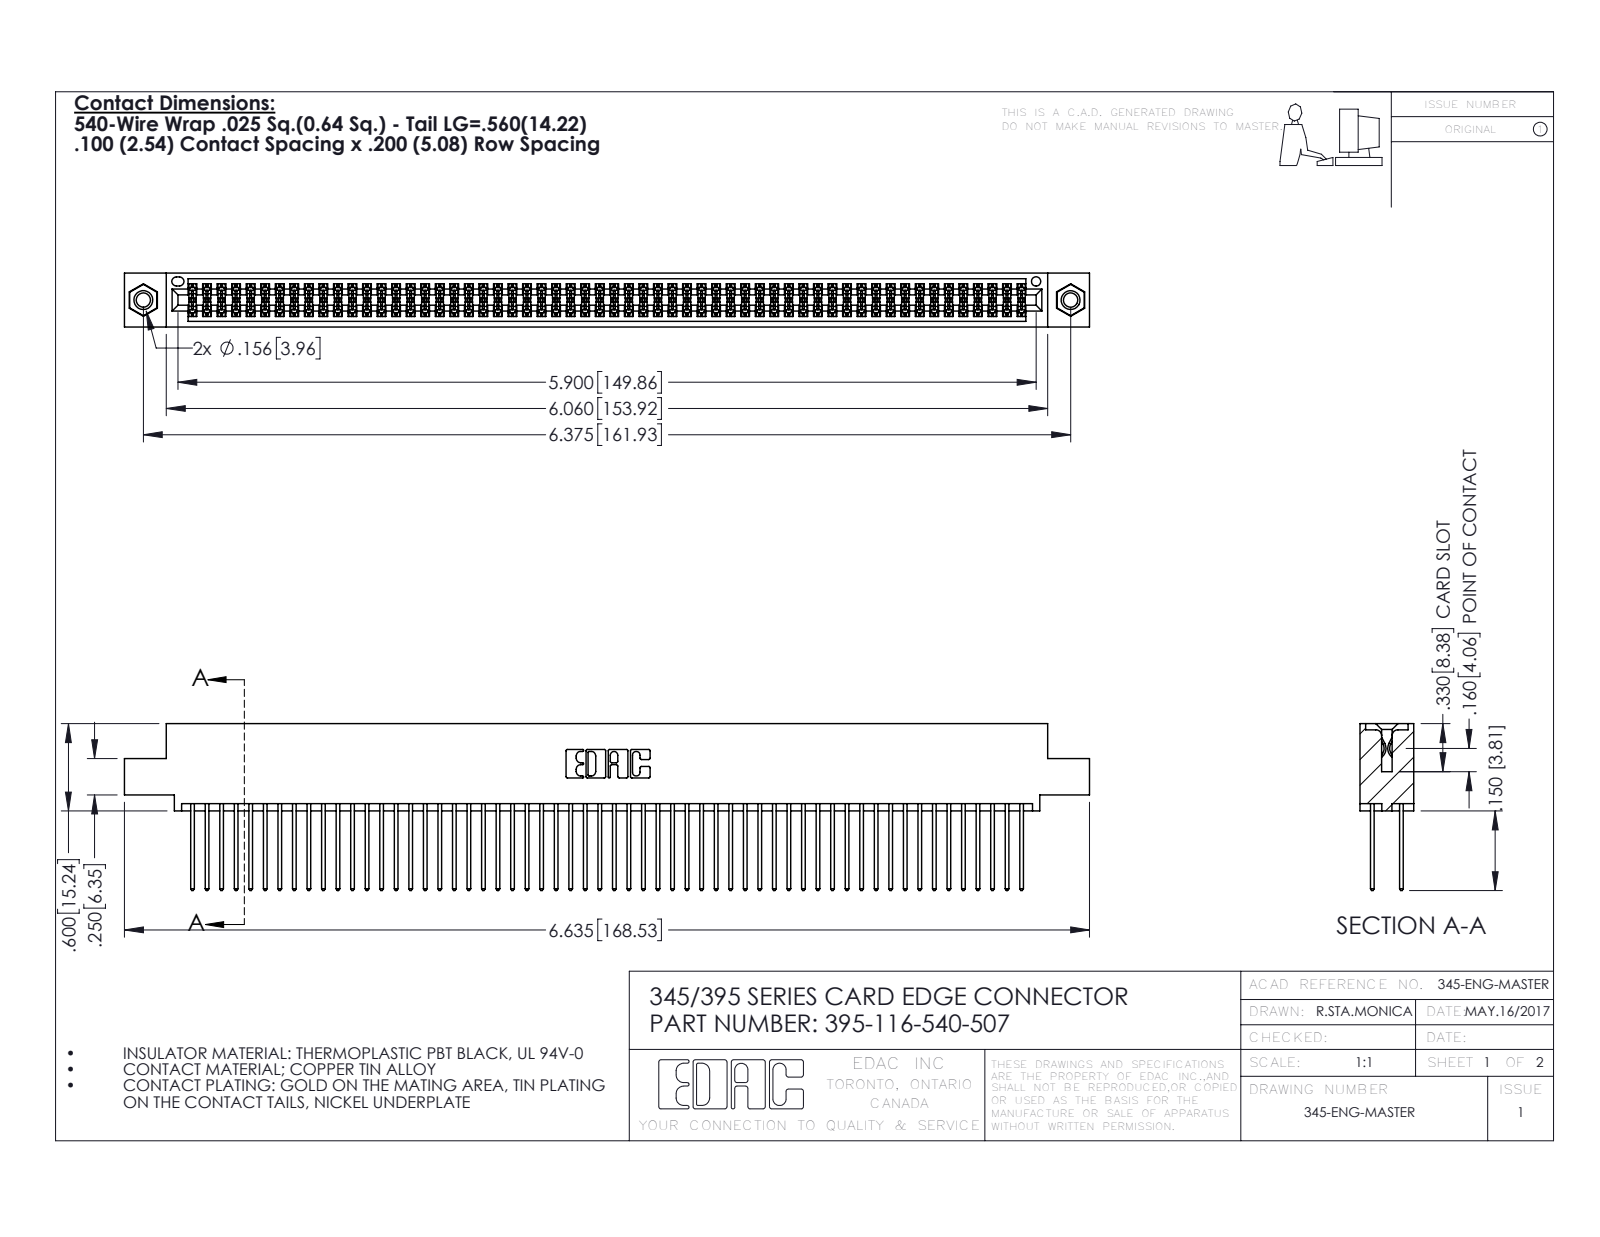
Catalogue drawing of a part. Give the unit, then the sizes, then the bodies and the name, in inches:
Units: inches
Overall size (bounding box): 6.635 × 1.147 × 0.37
Round holes (diameter × count): ⌀0.098 ×2, ⌀0.125 ×2, ⌀0.156 ×2, ⌀0.064 ×1
Round bosses / shafts (diameter × count): ⌀0.155 ×2
Partial cylindrical surfaces — rounded edges, fillets, slot ends (radius × count): R0.006 ×174, R0.01 ×116, R0.01 ×22, R0.007 ×6, R0.031 ×6, R0.026 ×3, R0.014 ×2, R0.019 ×2
Main face-to-face distances: 0.072, 0.298, 0.2, 0.098, 0.272, 0.025, 0.37, 0.225, 0.175, 0.149
Hole centre spacings: 0.27, 6.139, 6.375
Volume: 1.03 in³ · Surface area: 42.49 in²
Bodies: 119 solids, 5990 faces (3944 planar, 2030 cylindrical, 16 other)
Part name (STEP PRODUCT): 345 Part_0.110 Offset - 0.156 Dia-TI; 345-250-001_345-250-005-103; 395-116-540-507; 345-292-001_345-293-140
STEP written by: SolidWorks 2016 (CONFIG_CONTROL_DESIGN)
